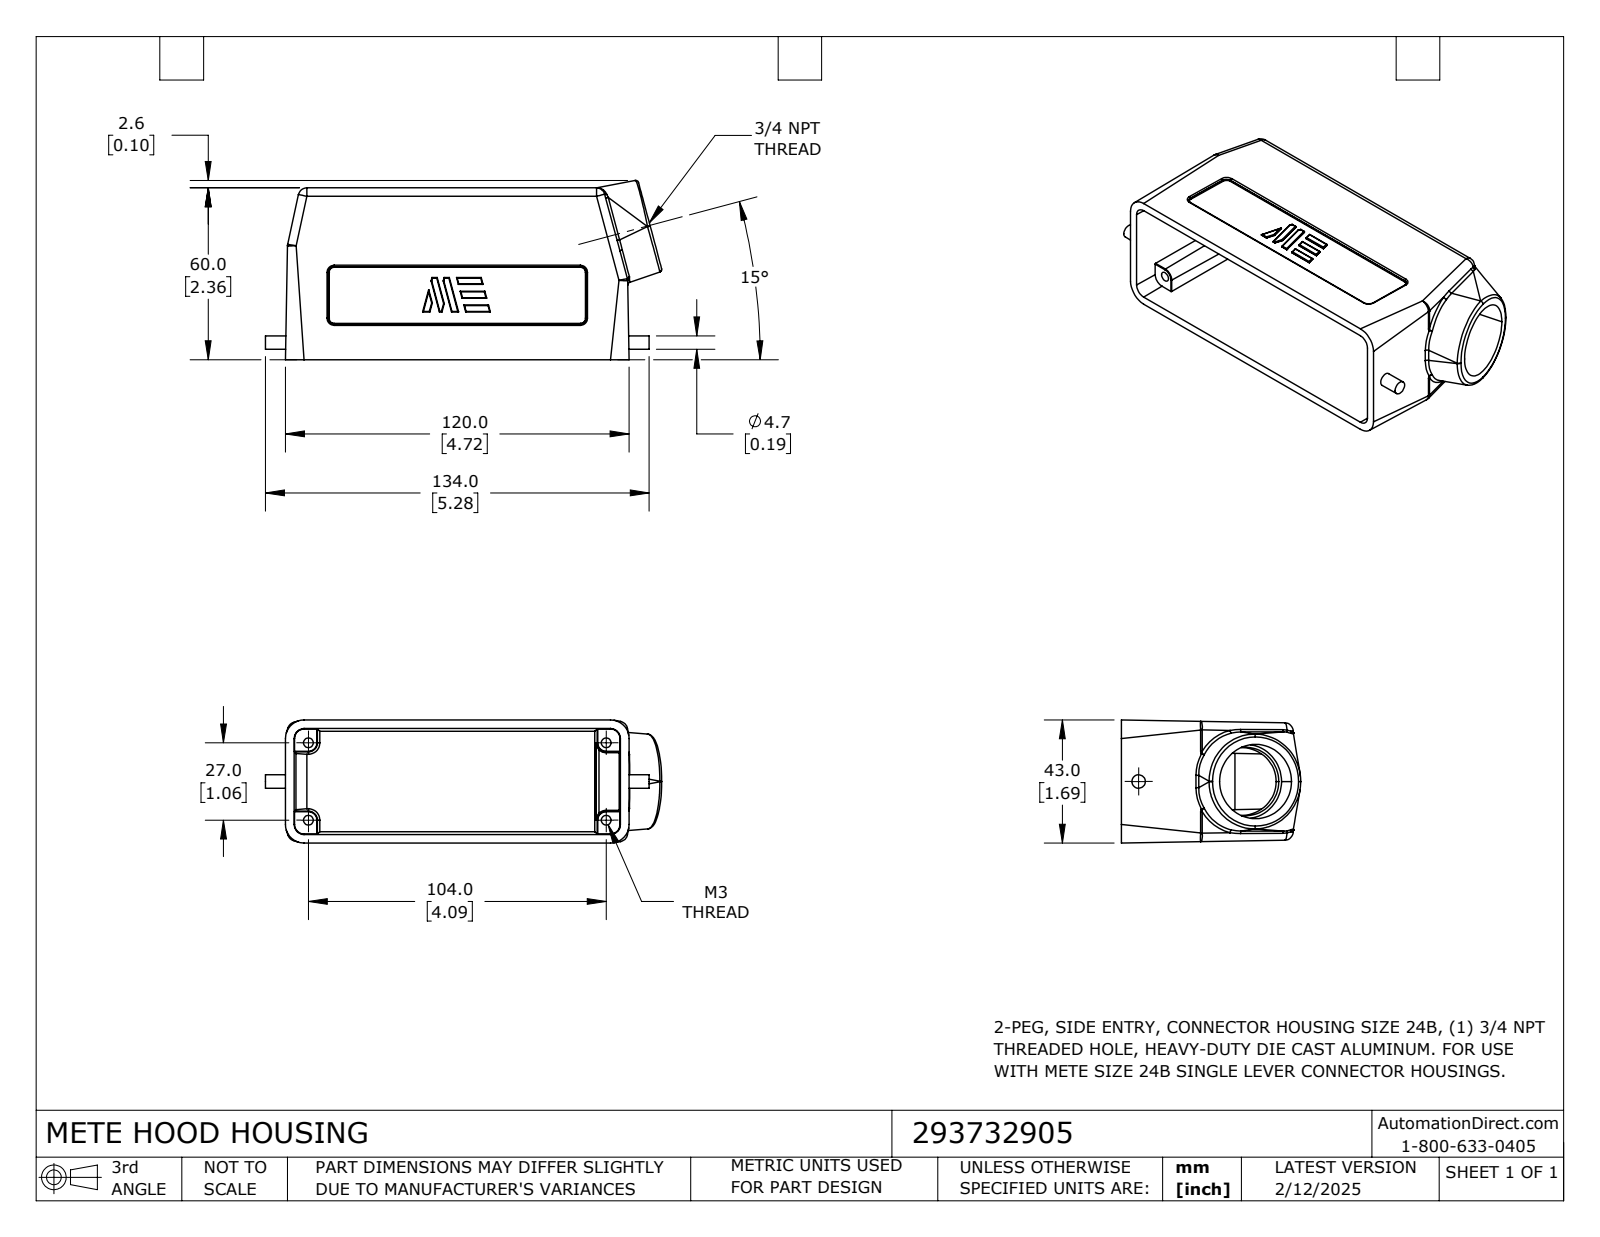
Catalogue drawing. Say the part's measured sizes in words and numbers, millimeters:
The part is named "293732905". Its 3-D file was written by "SolidWorks 2024 (CONFIG_CONTROL_DESIGN)". It is 1 solid with 302 faces: 115 planar, 115 cylindrical and 72 other. Overall it measures 138.4 by 62.6 by 43 millimeters. Its volume is 76 130 cubic millimeters and its surface area 46 090 square millimeters. Round holes: 4 of diameter 3.4. Round bosses or shafts: 1 of diameter 4.7. Partial cylindrical surfaces (rounded edges, fillets, slot ends): 46 of radius 0.2, 8 of radius 0.5, 8 of radius 2, 8 of radius 3, 4 of radius 1, 2 of radius 2.5, 2 of radius 13. The main face-to-face distances are 3, 2.2, 0.8, 11, 8, 57, 60, 10.2, 9, 48. The hole center spacings are 27, 104, 107.4.
